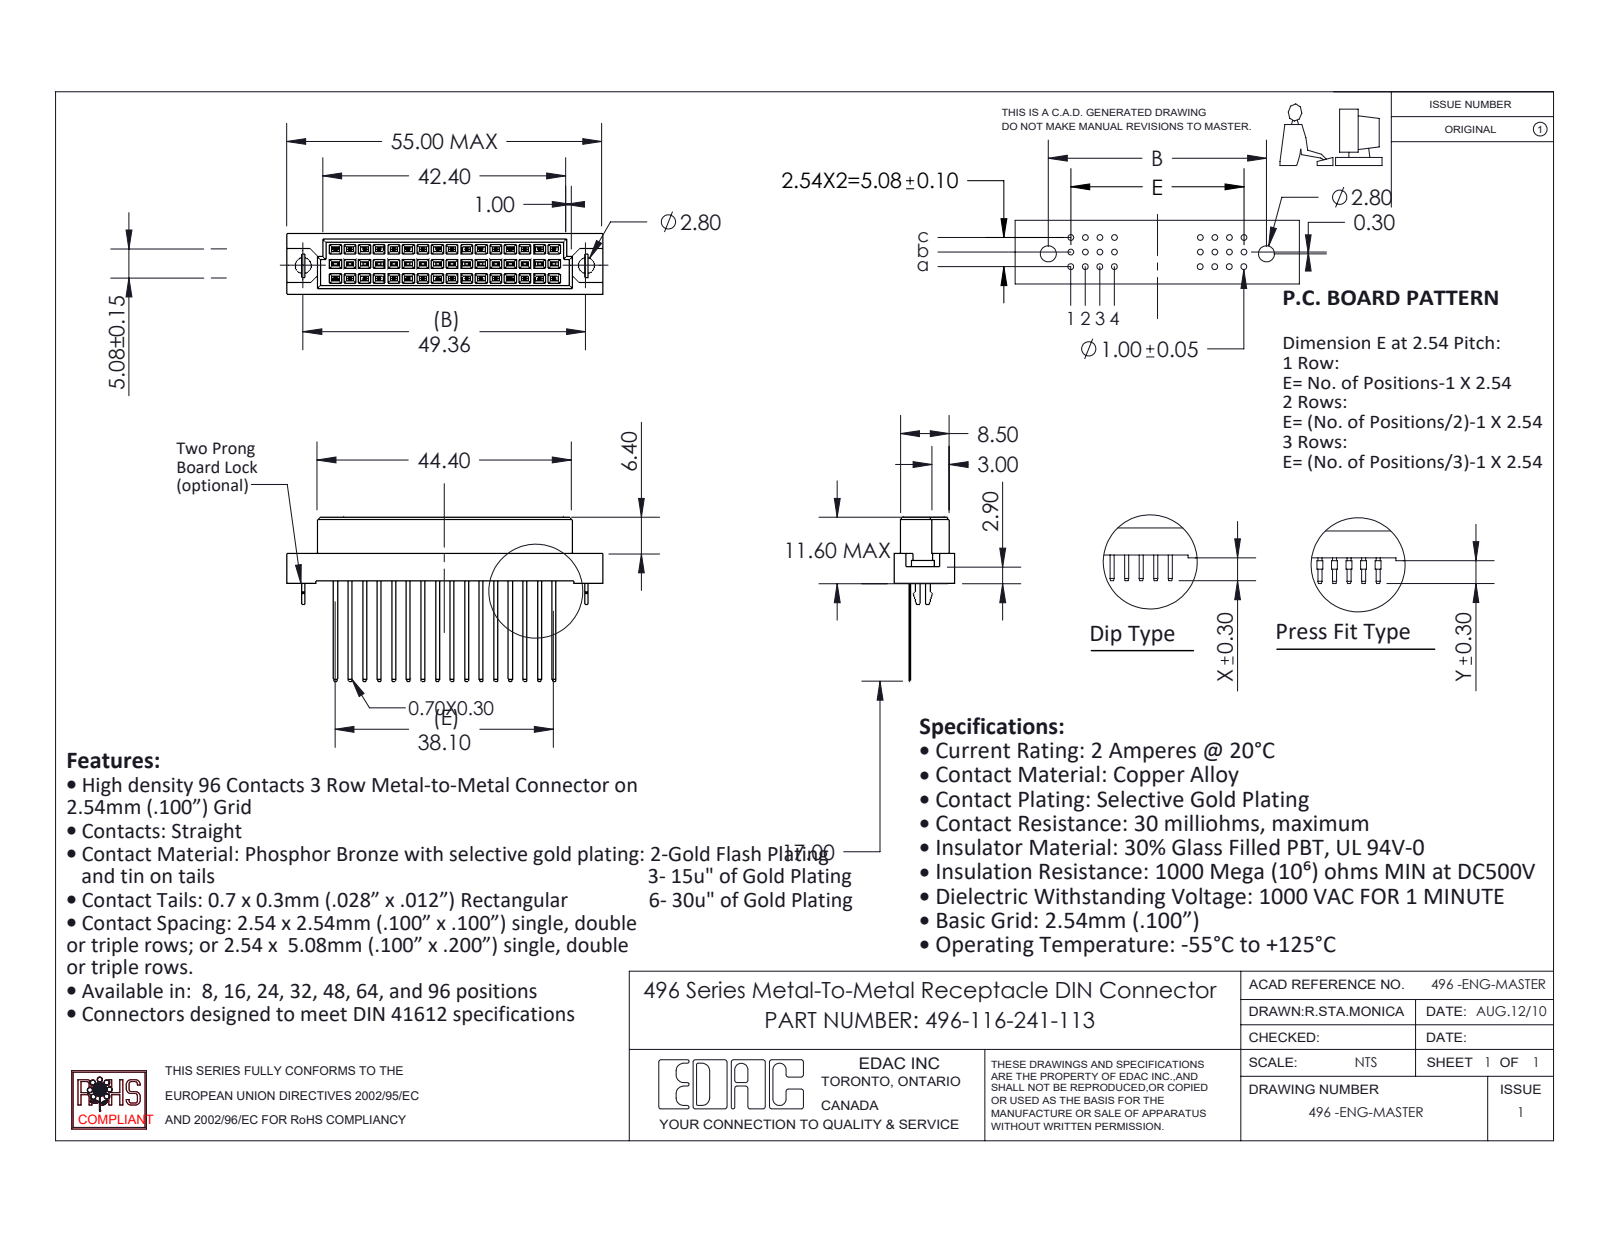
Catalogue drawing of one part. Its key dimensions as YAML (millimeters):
part_name: "496-116-241-113; 496 Part_48; 496 Bore-lock; 496-290_41"
step_written_by: "SolidWorks 2020 (CONFIG_CONTROL_DESIGN)"
units: millimeters
bodies: {solids: 19, faces: 862, planar: 856, cylindrical: 6, other: 0}
overall_size: [55, 28.6, 10.6]
volume: 4684
surface_area: 5017
round_holes:
  - {diameter: 2.8, count: 2}
partial_cylinders:
  - {radius: 0.53, count: 1}
face_to_face_distances: [2.54, 1.05, 9.55, 5.08, 0.81, 1.86, 1.56, 2.91, 7.69, 2.61]
hole_center_spacings: [49.36]
